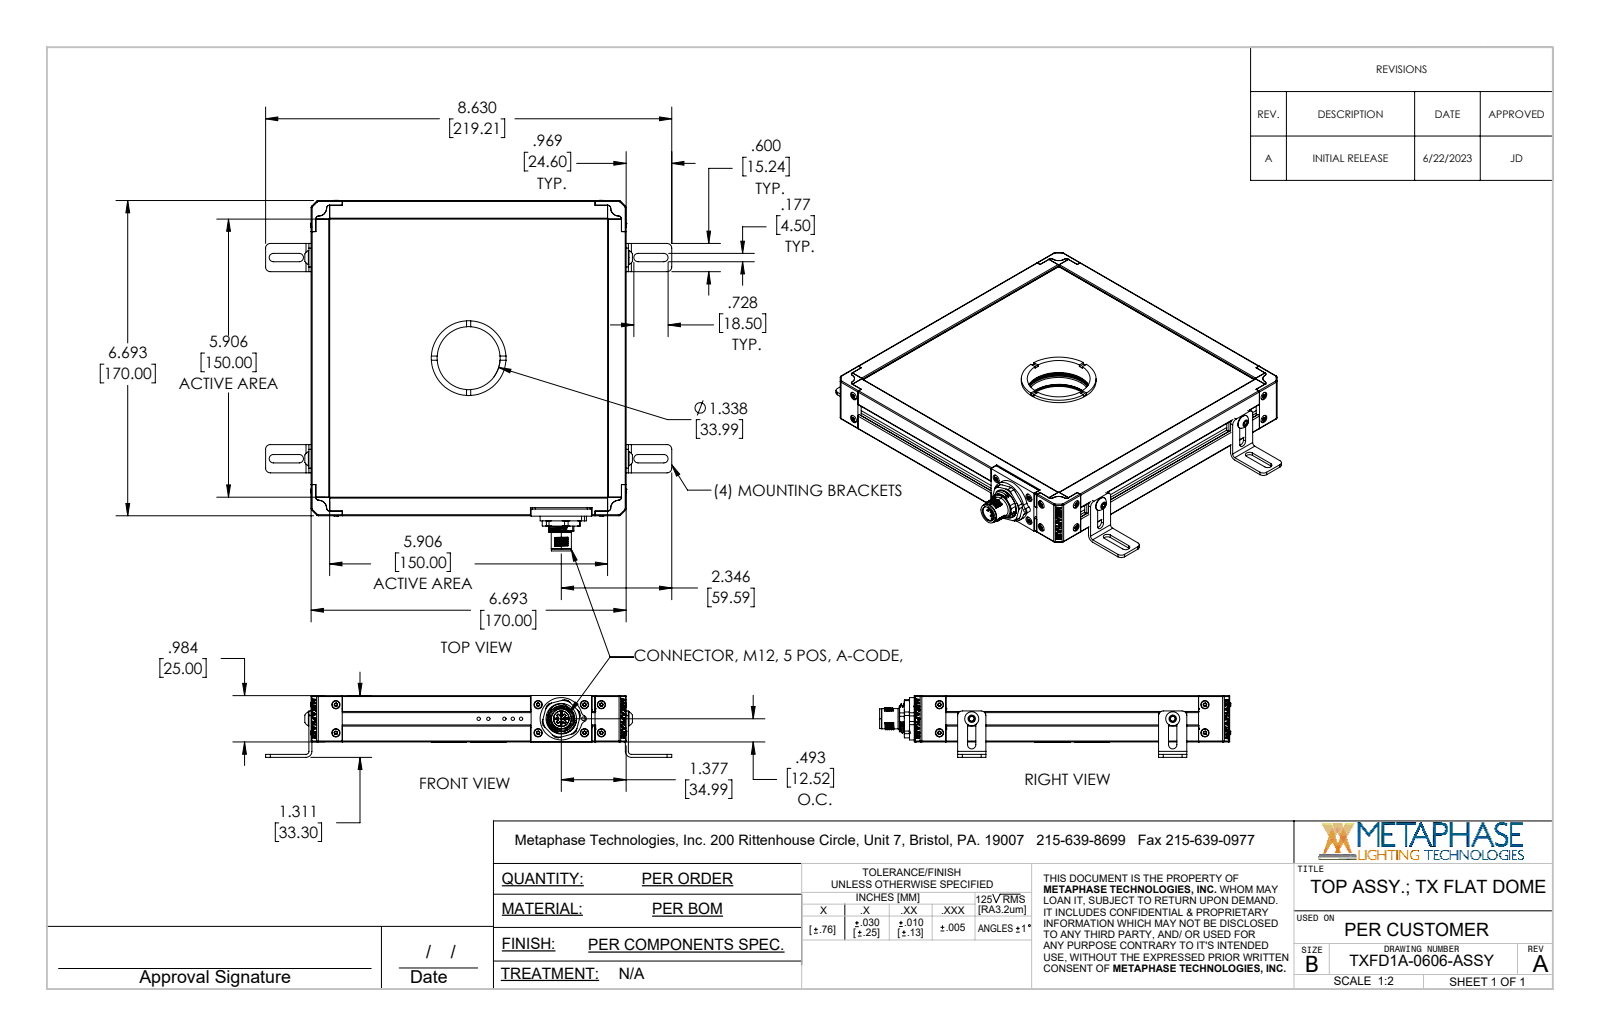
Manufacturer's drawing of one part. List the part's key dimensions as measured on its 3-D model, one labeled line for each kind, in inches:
Part name (STEP PRODUCT): TXBL-CORNER-SEAL; 50249_DEFAULT; 50459; TXBL-CONN-RAIL_TXBL-CONN-RAIL-06 (+8 more)
STEP written by: SolidWorks 2022 (CONFIG_CONTROL_DESIGN)
Units: inches
Bodies: 54 solids, 3052 faces (1310 planar, 1174 cylindrical, 568 other)
Overall size (bounding box): 8.63 × 7.444 × 1.312
Volume: 13.62 in³ · Surface area: 308.3 in²
Round holes (diameter × count): ⌀0.071 ×17, ⌀0.107 ×8, ⌀0.175 ×6, ⌀0.175 ×6, ⌀0.041 ×5, ⌀0.035 ×4, ⌀0.11 ×4, ⌀0.177 ×4, ⌀0.128 ×2, ⌀0.035 ×1, ⌀0.06 ×1, ⌀0.078 ×1
Round bosses / shafts (diameter × count): ⌀0.157 ×14, ⌀0.079 ×12, ⌀0.063 ×5, ⌀0.039 ×5, ⌀0.299 ×2, ⌀0.272 ×2, ⌀1.588 ×1, ⌀1.418 ×1
Partial cylindrical surfaces — rounded edges, fillets, slot ends (radius × count): R0.006 ×120, R0.014 ×120, R0.02 ×77, R0.05 ×24, R0.004 ×18, R0.063 ×18, R0.1 ×14, R0.089 ×12
Main face-to-face distances: 0.118, 0.74, 0.858, 0.08, 0.66, 0.778, 0.14, 0.263, 6.43, 0.06
Hole centre spacings: 5.642, 5.673, 0.359, 0.747, 4.966, 5.283, 5.316, 0.596
